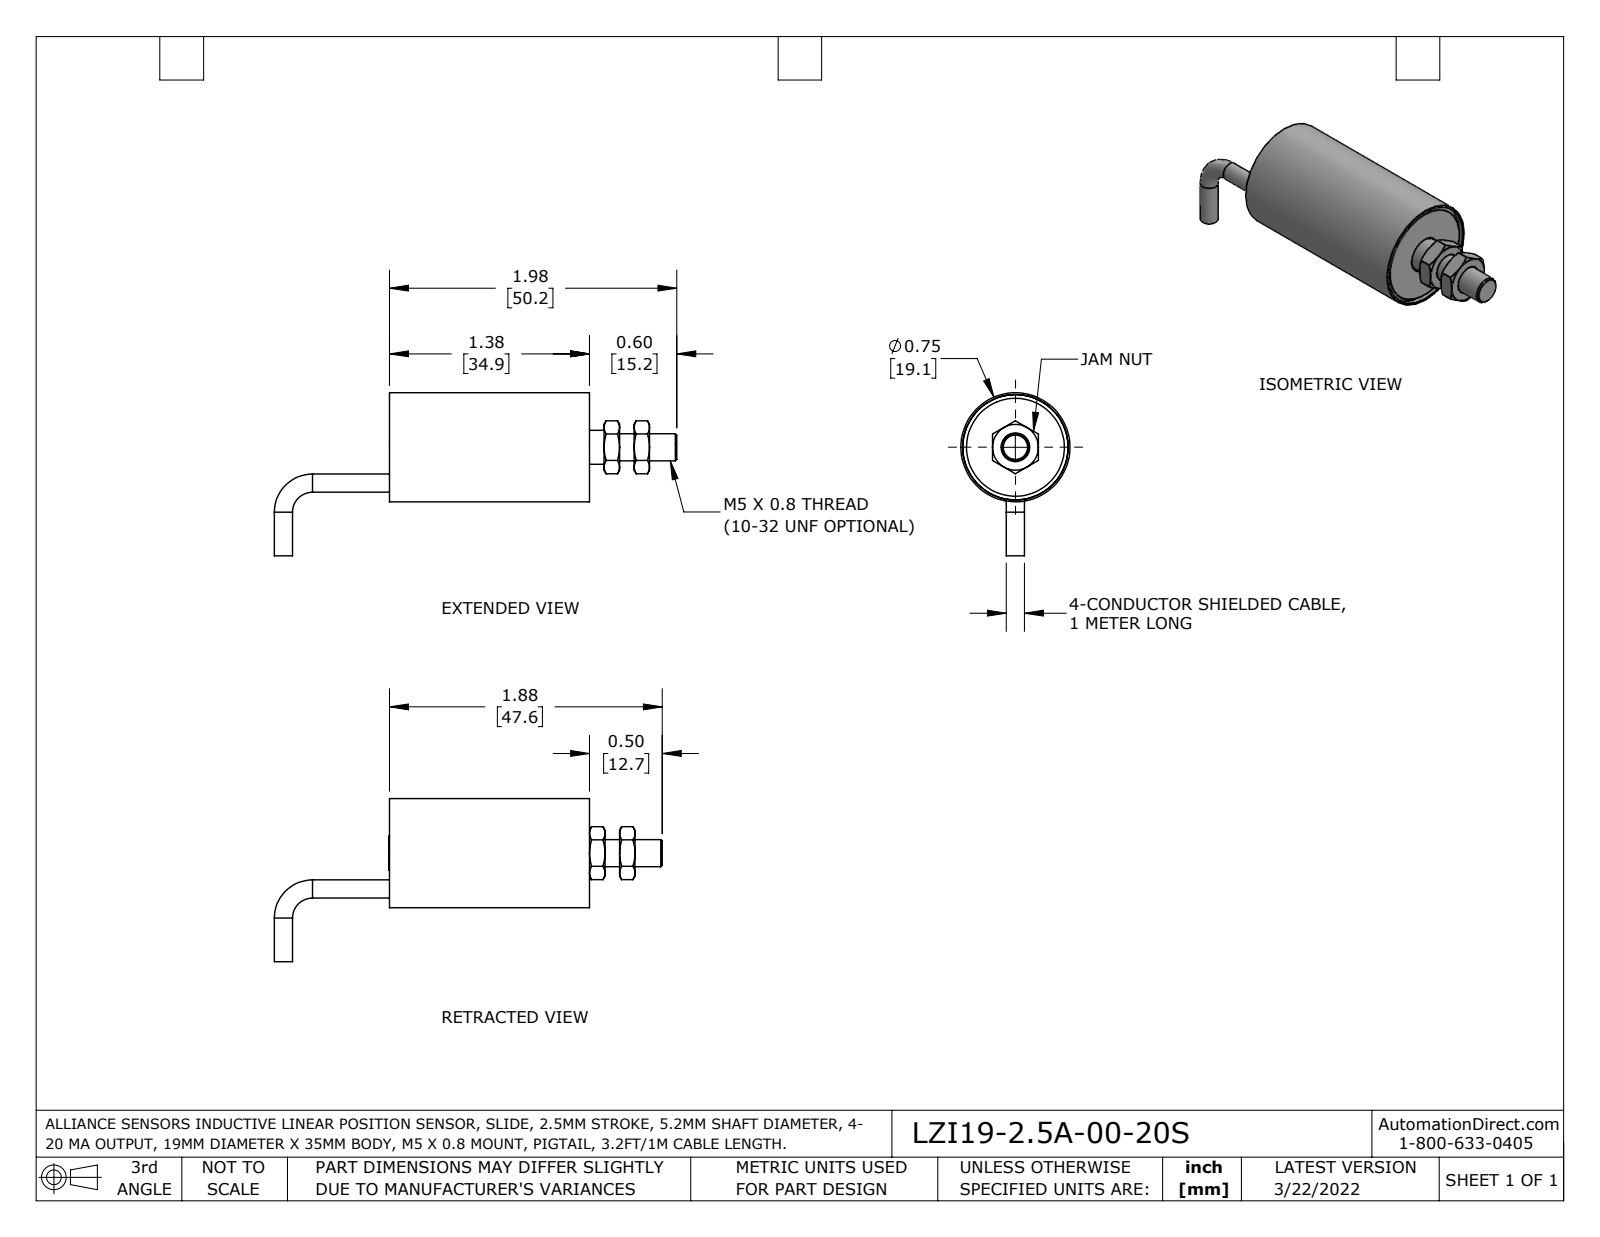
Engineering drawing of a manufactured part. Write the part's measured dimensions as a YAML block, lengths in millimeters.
part_name: "3120-0009-06_-01; 5300-0002; 3300-0008-06_-01; 3100-0076_B18.2.4.5M - Hex jam nut, M5 x 0.8 --D-N (+6 more)"
step_written_by: "SolidWorks 2021 (AUTOMOTIVE_DESIGN)"
units: millimeters
bodies: {solids: 10, faces: 137, planar: 42, cylindrical: 44, other: 51}
overall_size: [70.3, 28.5, 19.1]
volume: 4920
surface_area: 9968
round_holes:
  - {diameter: 4.2, count: 1}
  - {diameter: 4.8, count: 1}
  - {diameter: 5, count: 1}
  - {diameter: 5.9, count: 1}
  - {diameter: 7.1, count: 1}
  - {diameter: 17.3, count: 1}
  - {diameter: 18.4, count: 1}
round_bosses_or_shafts:
  - {diameter: 3.2, count: 2}
  - {diameter: 19.1, count: 1}
  - {diameter: 18.4, count: 1}
  - {diameter: 7.1, count: 1}
  - {diameter: 4.7, count: 1}
partial_cylinders:
  - {radius: 1.3, count: 1}
face_to_face_distances: [1.5, 32.9, 2, 31.4, 34.4, 5.2, 8, 2.5, 2.7, 9.5]
